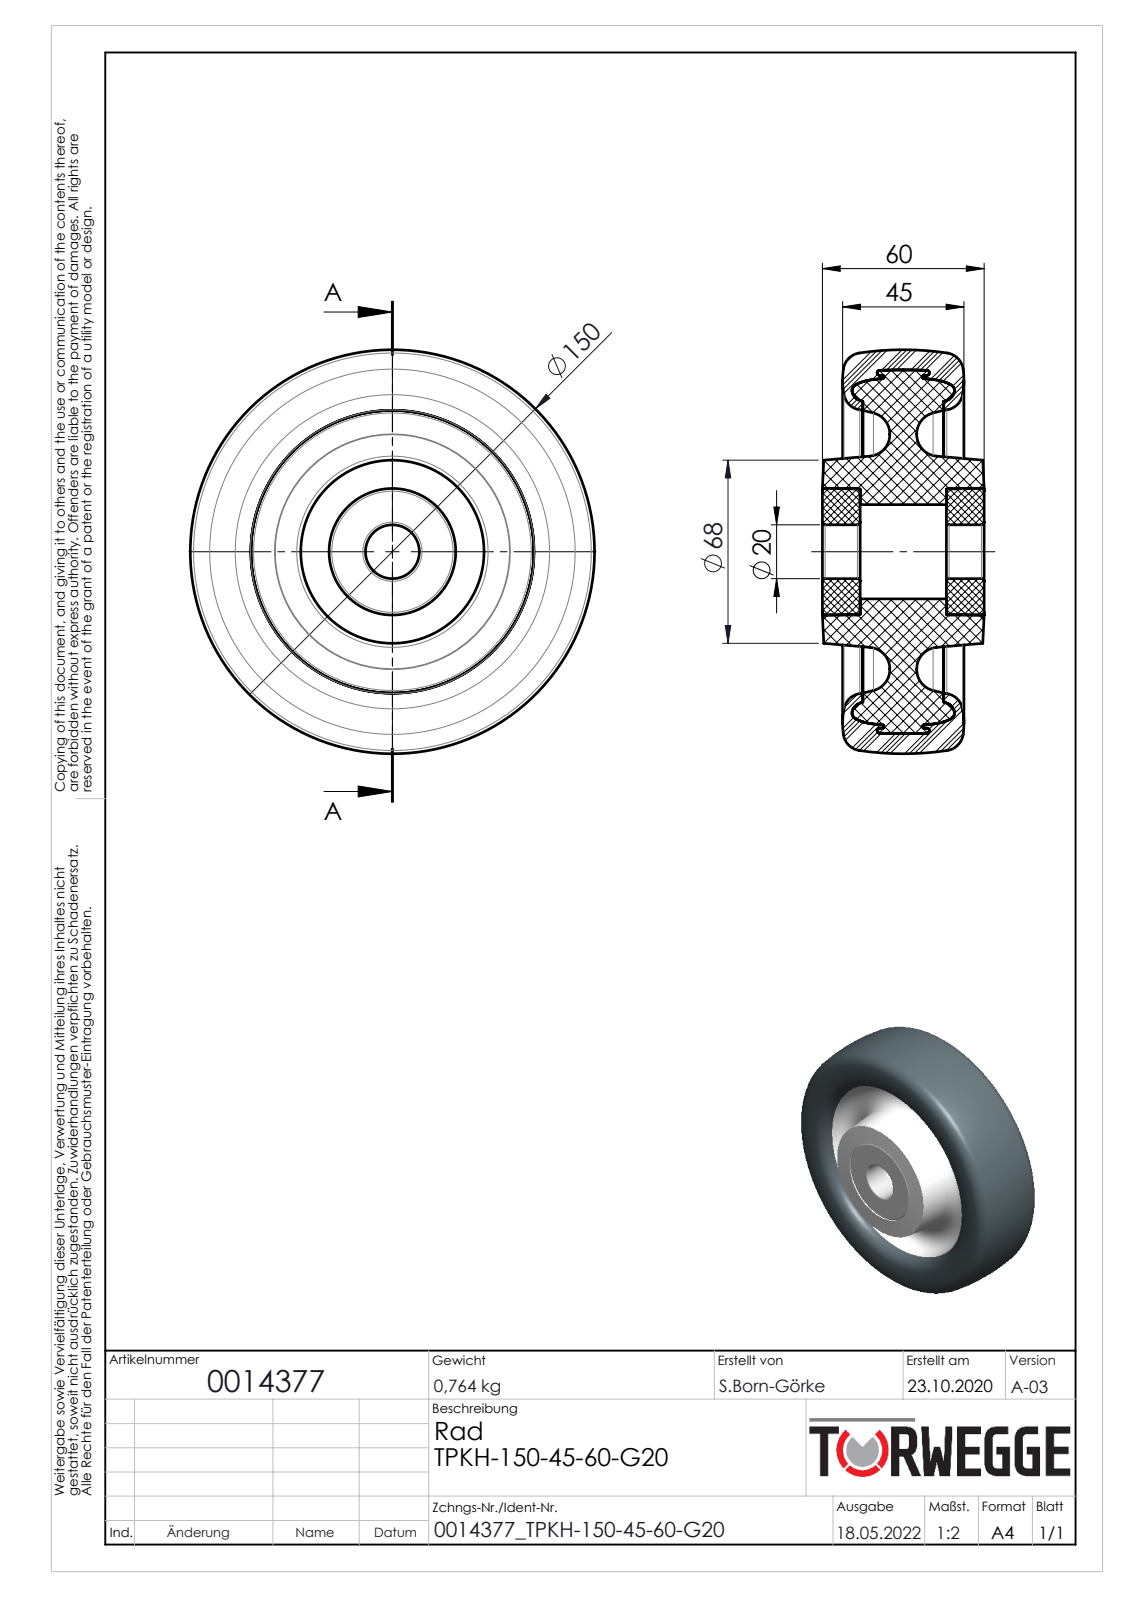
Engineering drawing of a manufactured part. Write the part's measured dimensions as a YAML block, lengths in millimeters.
part_name: "0014377"
step_written_by: "SolidWorks 2020 (AUTOMOTIVE_DESIGN)"
units: millimeters
bodies: {solids: 3, faces: 76, planar: 8, cylindrical: 10, other: 58}
overall_size: [150, 149.95, 60]
volume: 629372
surface_area: 84412
round_holes:
  - {diameter: 20, count: 1}
  - {diameter: 35, count: 1}
round_bosses_or_shafts:
  - {diameter: 47, count: 1}
face_to_face_distances: [14, 46, 32, 60, 25, 35, 11, 21, 10]
